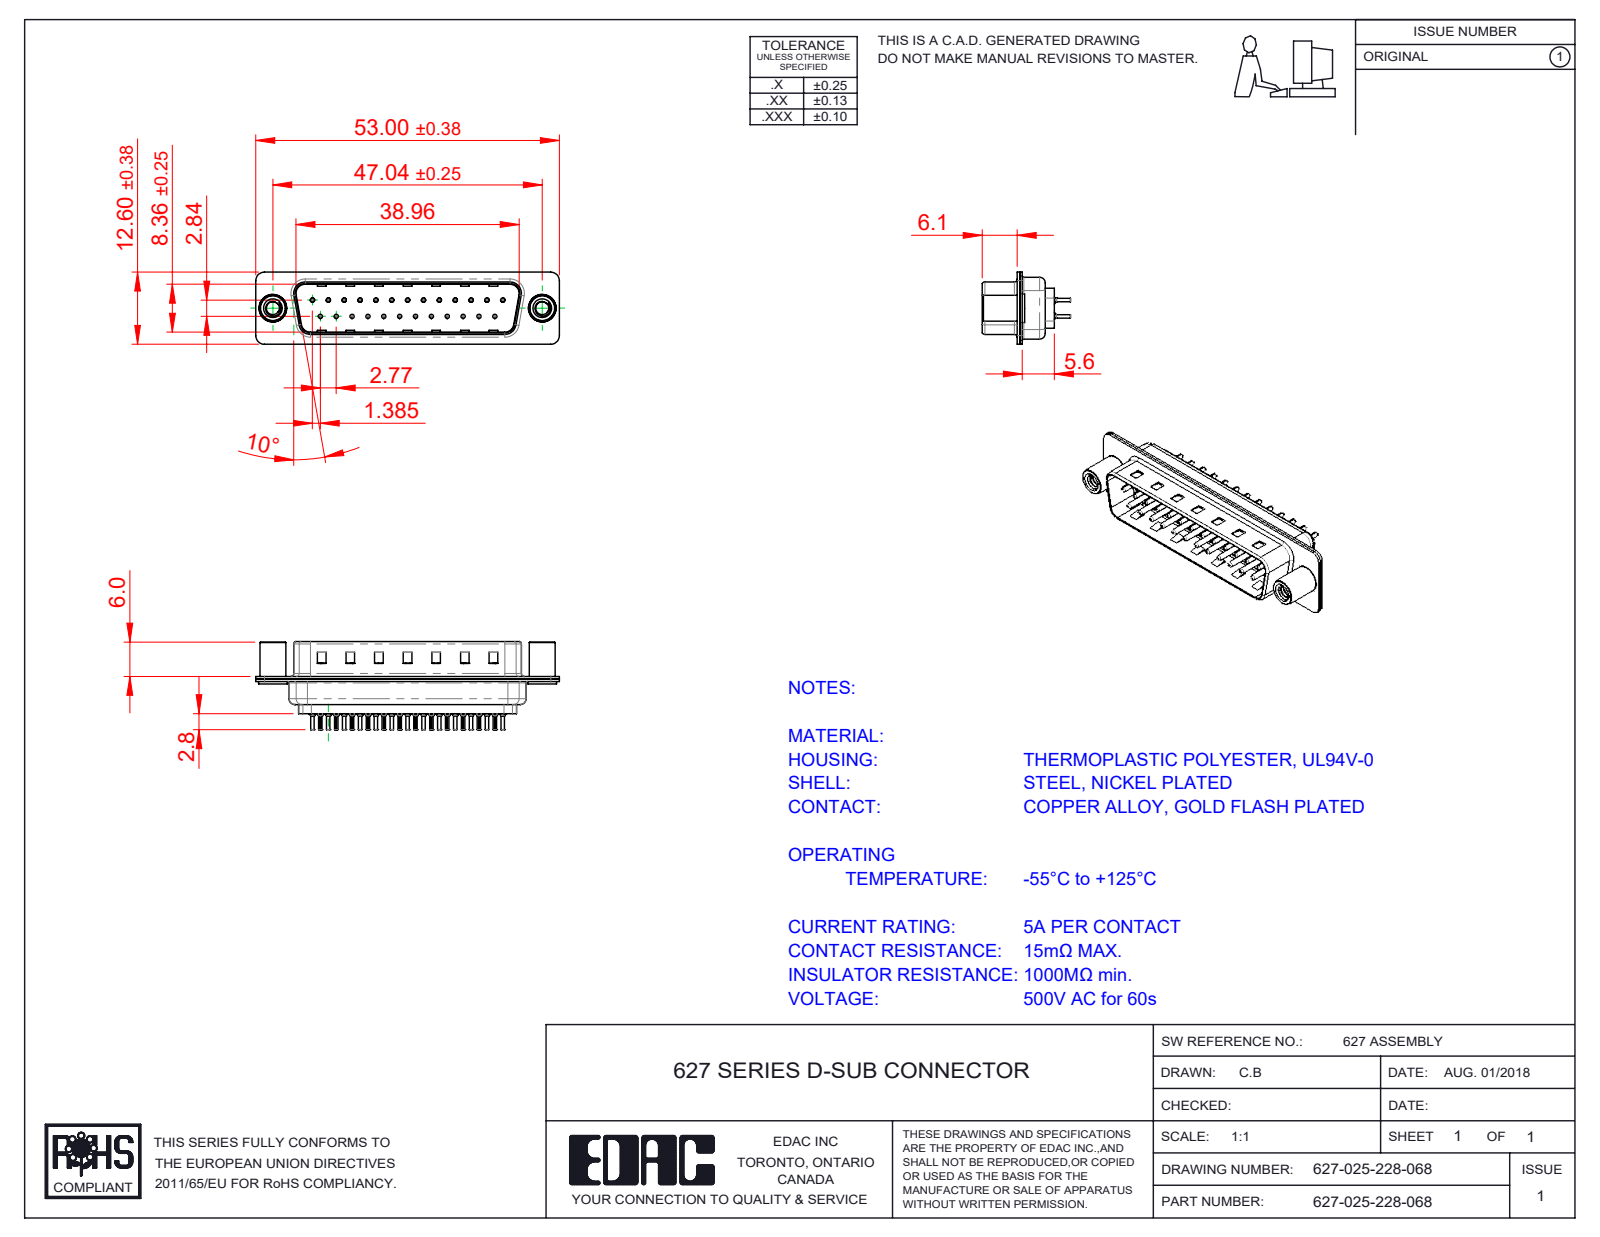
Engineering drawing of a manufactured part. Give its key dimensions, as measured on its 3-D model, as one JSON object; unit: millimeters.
{"part_name": "627 Contact Row 2_28L; 627 4-40 Threaded Standoff; 627 Shell Front_25 Contacts; 627-025-228-068 (+3 more)", "step_written_by": "SolidWorks 2020 (CONFIG_CONTROL_DESIGN)", "units": "millimeters", "bodies": {"solids": 31, "faces": 2921, "planar": 779, "cylindrical": 1145, "other": 997}, "overall_size": [53, 18.8, 12.6], "volume_mm3": 3341, "surface_area_mm2": 9119, "round_holes": [[0.2, 25], [0.35, 25], [1.1, 25], [1.6, 25], [2.26, 2], [4, 2], [4.8, 2]], "round_bosses_or_shafts": [[2, 25], [1.5, 25], [0.75, 25], [0.6, 25], [5, 2], [4.9, 2], [4.5, 2]], "partial_cylinders_radius": [[0.1, 50], [1.5, 16], [2, 12], [0.5, 8], [1.6, 8], [0.25, 4], [0.6, 4], [0.65, 4]], "face_to_face_distances": [0.4, 0.45, 6.05, 0.82, 9.58, 8.4, 0.9, 1.5, 0.68, 7.68], "hole_center_spacings": [3.16, 2.77, 5.54, 8.31, 11.08, 13.85, 5.04, 7.49]}
